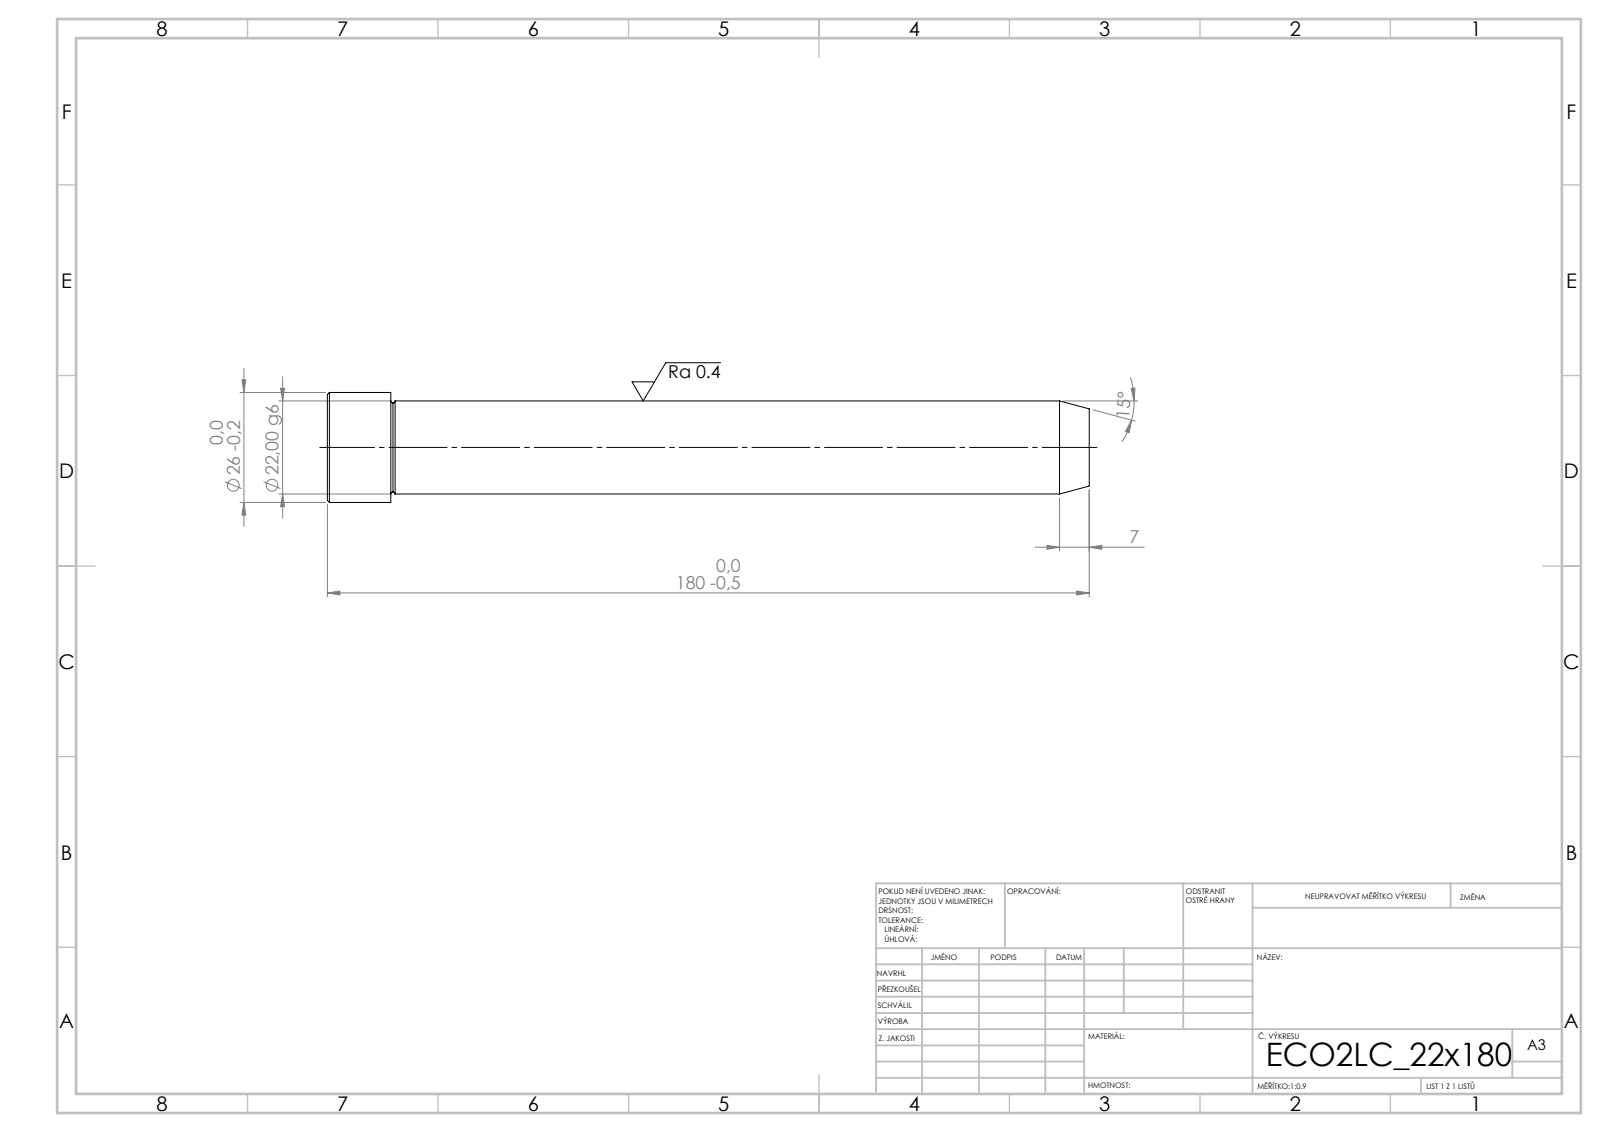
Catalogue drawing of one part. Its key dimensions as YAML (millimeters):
step_written_by: "SolidWorks 2019 (CONFIG_CONTROL_DESIGN)"
units: millimeters
bodies: {solids: 1, faces: 15, planar: 3, cylindrical: 4, other: 8}
overall_size: [180, 26, 26]
volume: 70221
surface_area: 13559
round_bosses_or_shafts:
  - {diameter: 26, count: 1}
  - {diameter: 22, count: 1}
face_to_face_distances: [180, 165, 15]
